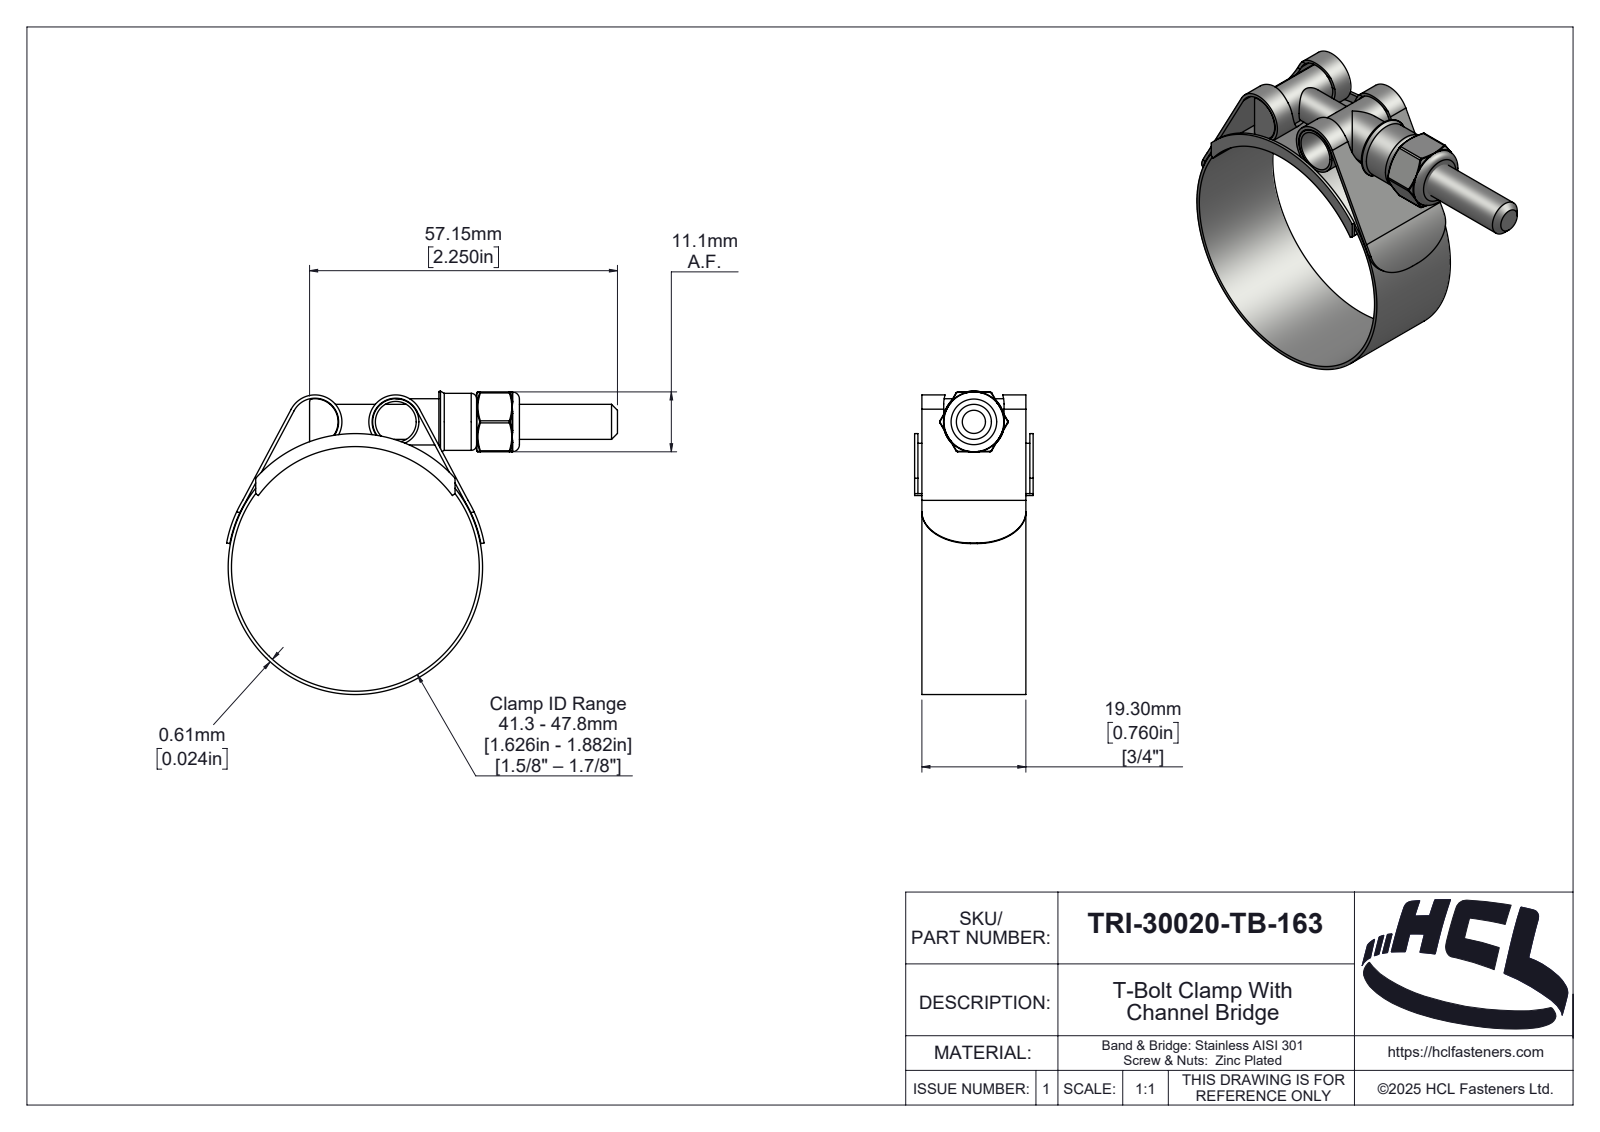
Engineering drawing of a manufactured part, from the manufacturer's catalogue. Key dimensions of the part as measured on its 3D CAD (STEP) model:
Part name (STEP PRODUCT): TRI-30020-TB-163
STEP written by: SolidWorks 2025 (AUTOMOTIVE_DESIGN)
Units: millimetres
Bodies: 6 solids, 338 faces (48 planar, 126 cylindrical, 164 other)
Overall size (bounding box): 72.55 × 56.31 × 22
Volume: 6 743 mm³ · Surface area: 14 292 mm²
Round holes (diameter × count): ⌀5.4 ×1, ⌀6.35 ×1, ⌀6.5 ×1, ⌀7.58 ×1, ⌀46 ×1
Round bosses / shafts (diameter × count): ⌀8.58 ×2, ⌀47.22 ×1, ⌀10.58 ×1
Partial cylindrical surfaces — rounded edges, fillets, slot ends (radius × count): R0.39 ×6, R0.5 ×2, R4.39 ×2, R5 ×2, R5.6 ×2, R0.59 ×1, R2.42 ×1, R3.03 ×1
Main face-to-face distances: 0.61, 0.74, 1.35, 20.65, 19.3, 21.39, 20.04, 11.11, 22, 31
Hole centre spacings: 28
